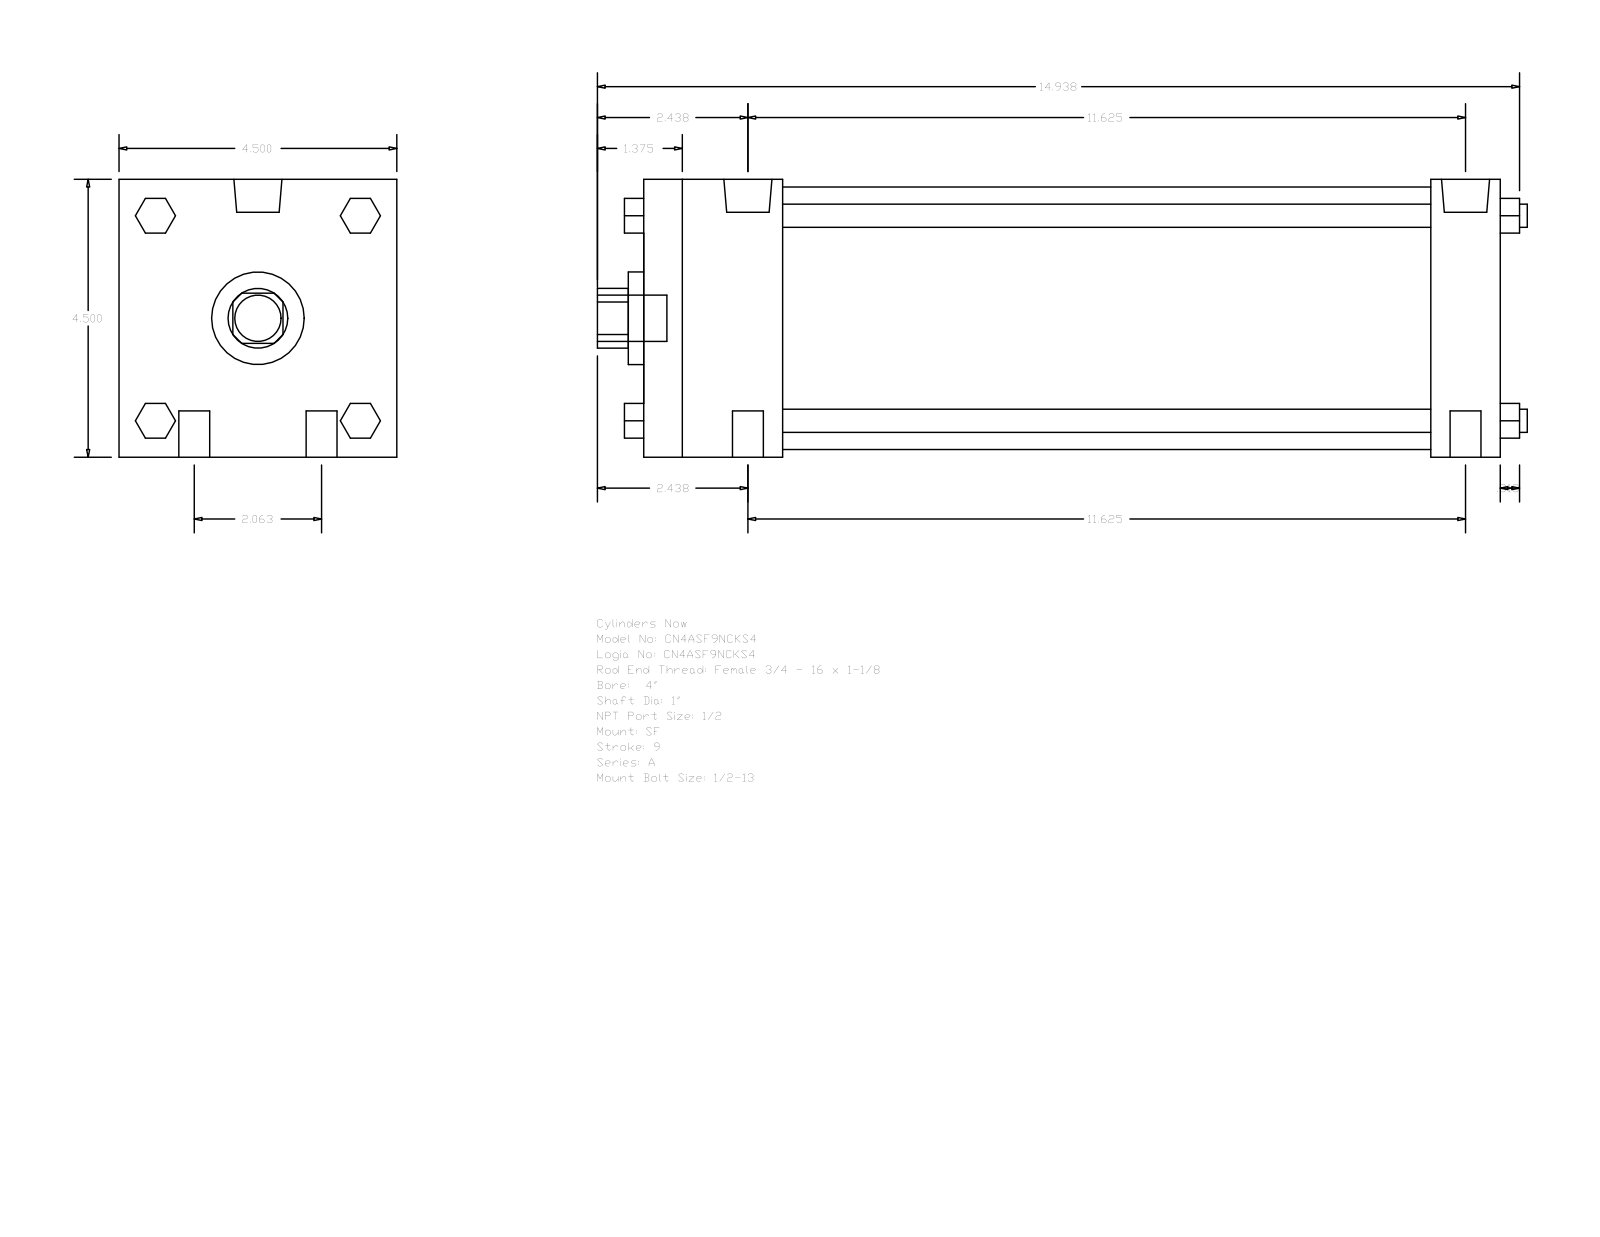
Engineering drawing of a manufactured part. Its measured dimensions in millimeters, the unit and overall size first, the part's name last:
Units: millimetres
Overall size (bounding box): 382.59 × 114.3 × 114.3
Round holes (diameter × count): ⌀25.4 ×1, ⌀38.1 ×1, ⌀107.95 ×1
Round bosses / shafts (diameter × count): ⌀12.7 ×4, ⌀9.53 ×4, ⌀19.77 ×2, ⌀8.73 ×2, ⌀19.05 ×1
Partial cylindrical surfaces — rounded edges, fillets, slot ends (radius × count): R12.29 ×1
Main face-to-face distances: 114.3, 352.43, 323.85, 28.58, 57.15, 266.7, 295.28, 14.29, 42.16, 73.03
Bodies: 0 solids, 124 faces (94 planar, 30 cylindrical, 0 other)
Part name (STEP PRODUCT): A_SF__0400_1
STEP written by: GSSL Pune (CONFIG_CONTROL_DESIGN)
